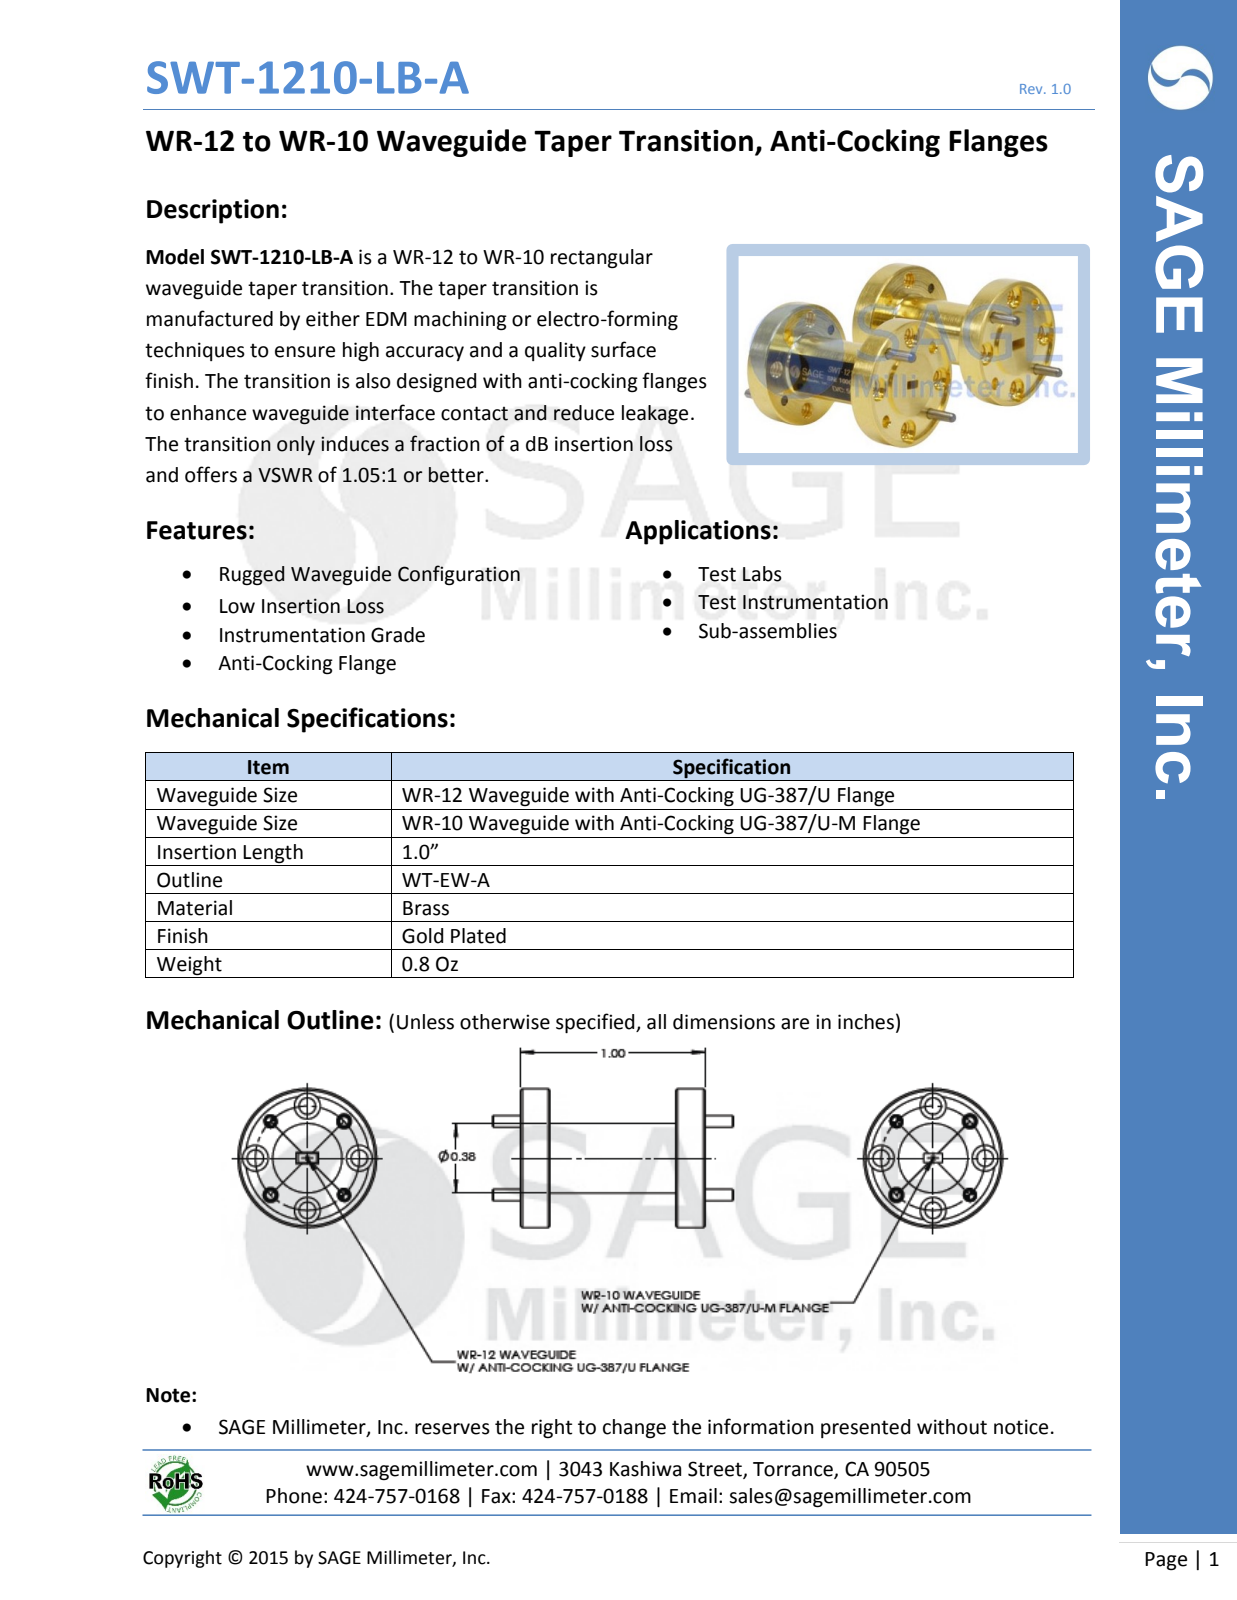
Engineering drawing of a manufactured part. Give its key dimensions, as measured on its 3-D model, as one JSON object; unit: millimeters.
{"part_name": "DMWT-EW-301-A", "step_written_by": "SolidWorks 2013 (CONFIG_CONTROL_DESIGN)", "units": "millimeters", "bodies": {"solids": 5, "faces": 142, "planar": 28, "cylindrical": 74, "other": 40}, "overall_size": [33.1, 19.1, 19.1], "volume_mm3": 3130, "surface_area_mm2": 2699, "round_holes": [[1.5, 4], [1.7, 4], [2.3, 4], [3.6, 4], [17.3, 1]], "round_bosses_or_shafts": [[1.6, 4], [19.1, 1], [9.5, 1], [9.5, 1]], "face_to_face_distances": [3.6, 20.8, 17.3, 24.4, 24.9, 21.3, 4.1, 0.5, 0.5, 4.1], "hole_center_spacings": [5.5, 10.1, 7.1, 13.2, 13.2, 7.1, 14.3, 14.3]}
